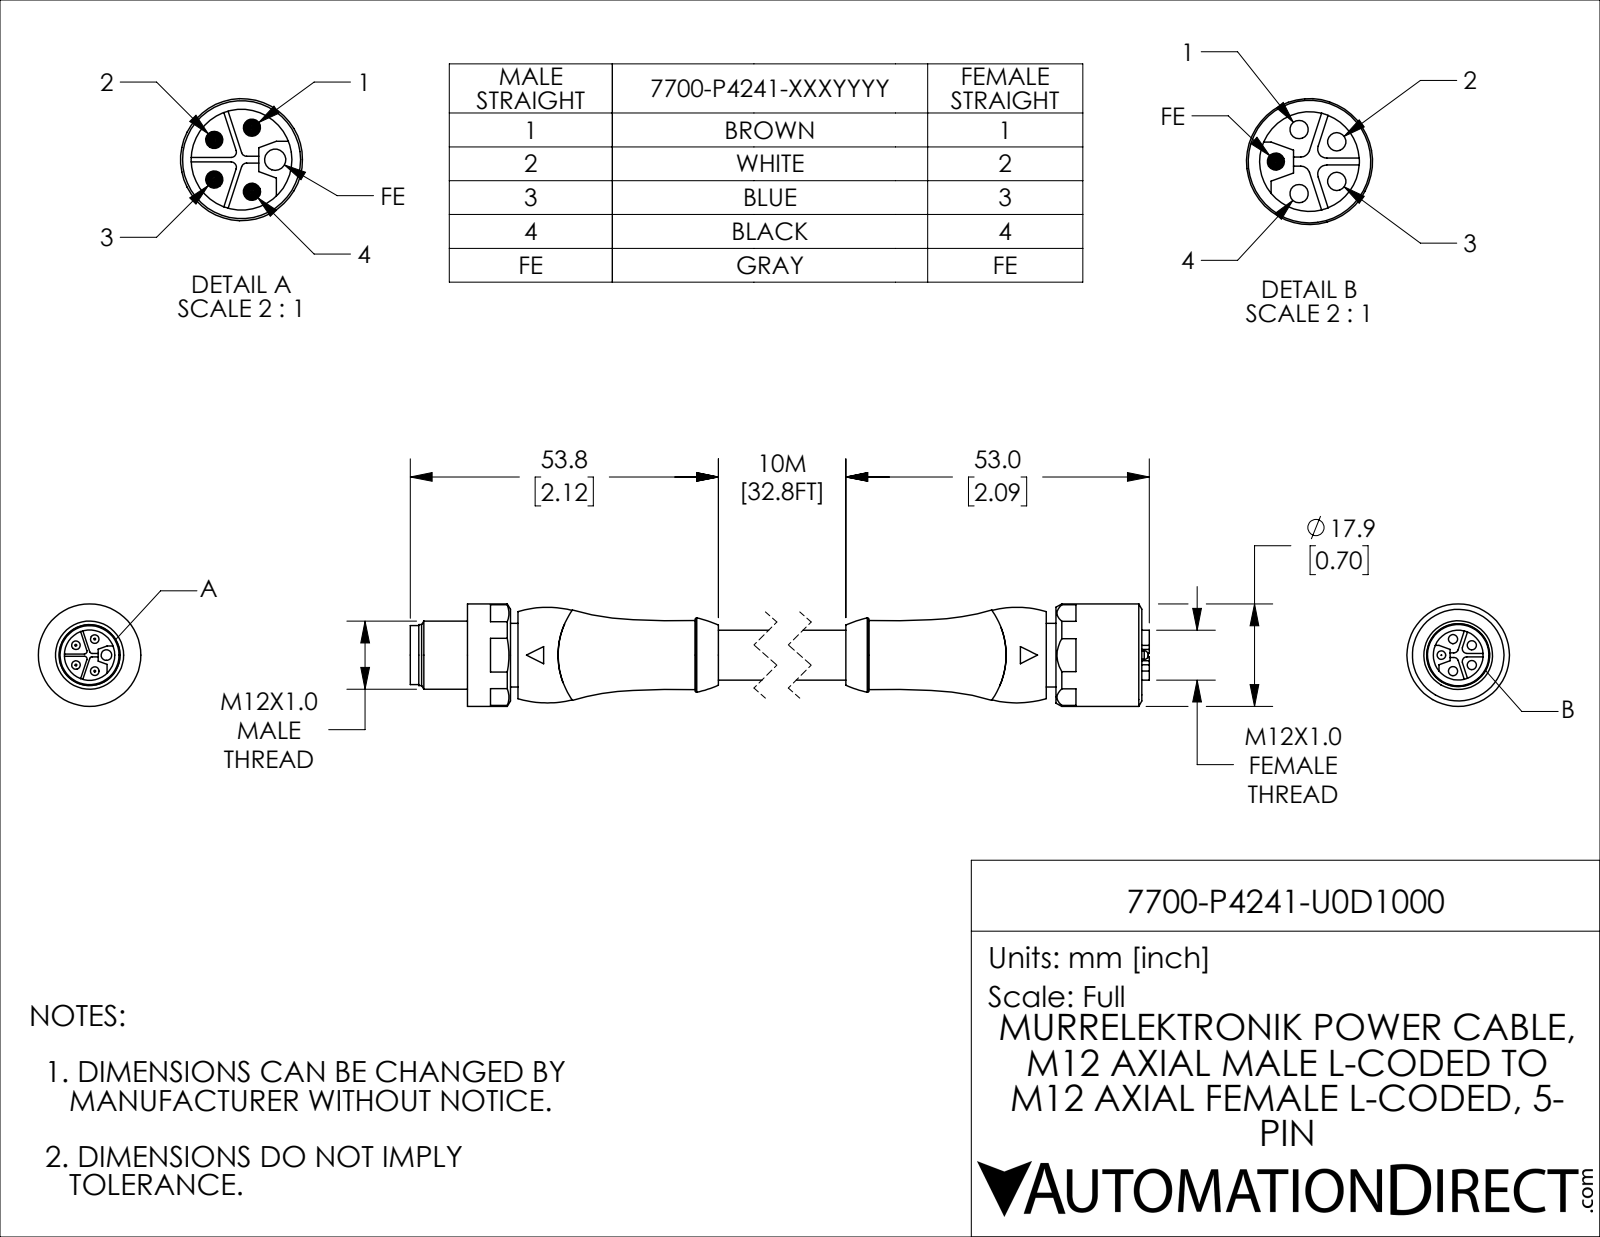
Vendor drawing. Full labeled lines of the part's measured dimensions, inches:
Part name (STEP PRODUCT): 7700-P4241-U0D1000_1; 7700-P4241-U0D1000_2; 7700-P4241-U0D1000
STEP written by: SolidWorks 2021 (CONFIG_CONTROL_DESIGN)
Units: inches
Bodies: 3 solids, 214 faces (98 planar, 62 cylindrical, 54 other)
Overall size (bounding box): 5.386 × 0.705 × 0.705
Volume: 1.09 in³ · Surface area: 14.44 in²
Round holes (diameter × count): ⌀0.063 ×4, ⌀0.073 ×1, ⌀0.346 ×1, ⌀0.433 ×1, ⌀0.512 ×1
Round bosses / shafts (diameter × count): ⌀0.059 ×5, ⌀0.705 ×1, ⌀0.51 ×1, ⌀0.469 ×1, ⌀0.437 ×1, ⌀0.419 ×1, ⌀0.406 ×1, ⌀0.343 ×1
Partial cylindrical surfaces — rounded edges, fillets, slot ends (radius × count): R0.018 ×4, R0.031 ×4
Main face-to-face distances: 4.283, 0.067, 0.346, 0.666, 0.051, 0.295, 0.228, 4.941, 0.657, 4.35
Hole centre spacings: 0.116, 0.136, 0.22, 0.22
